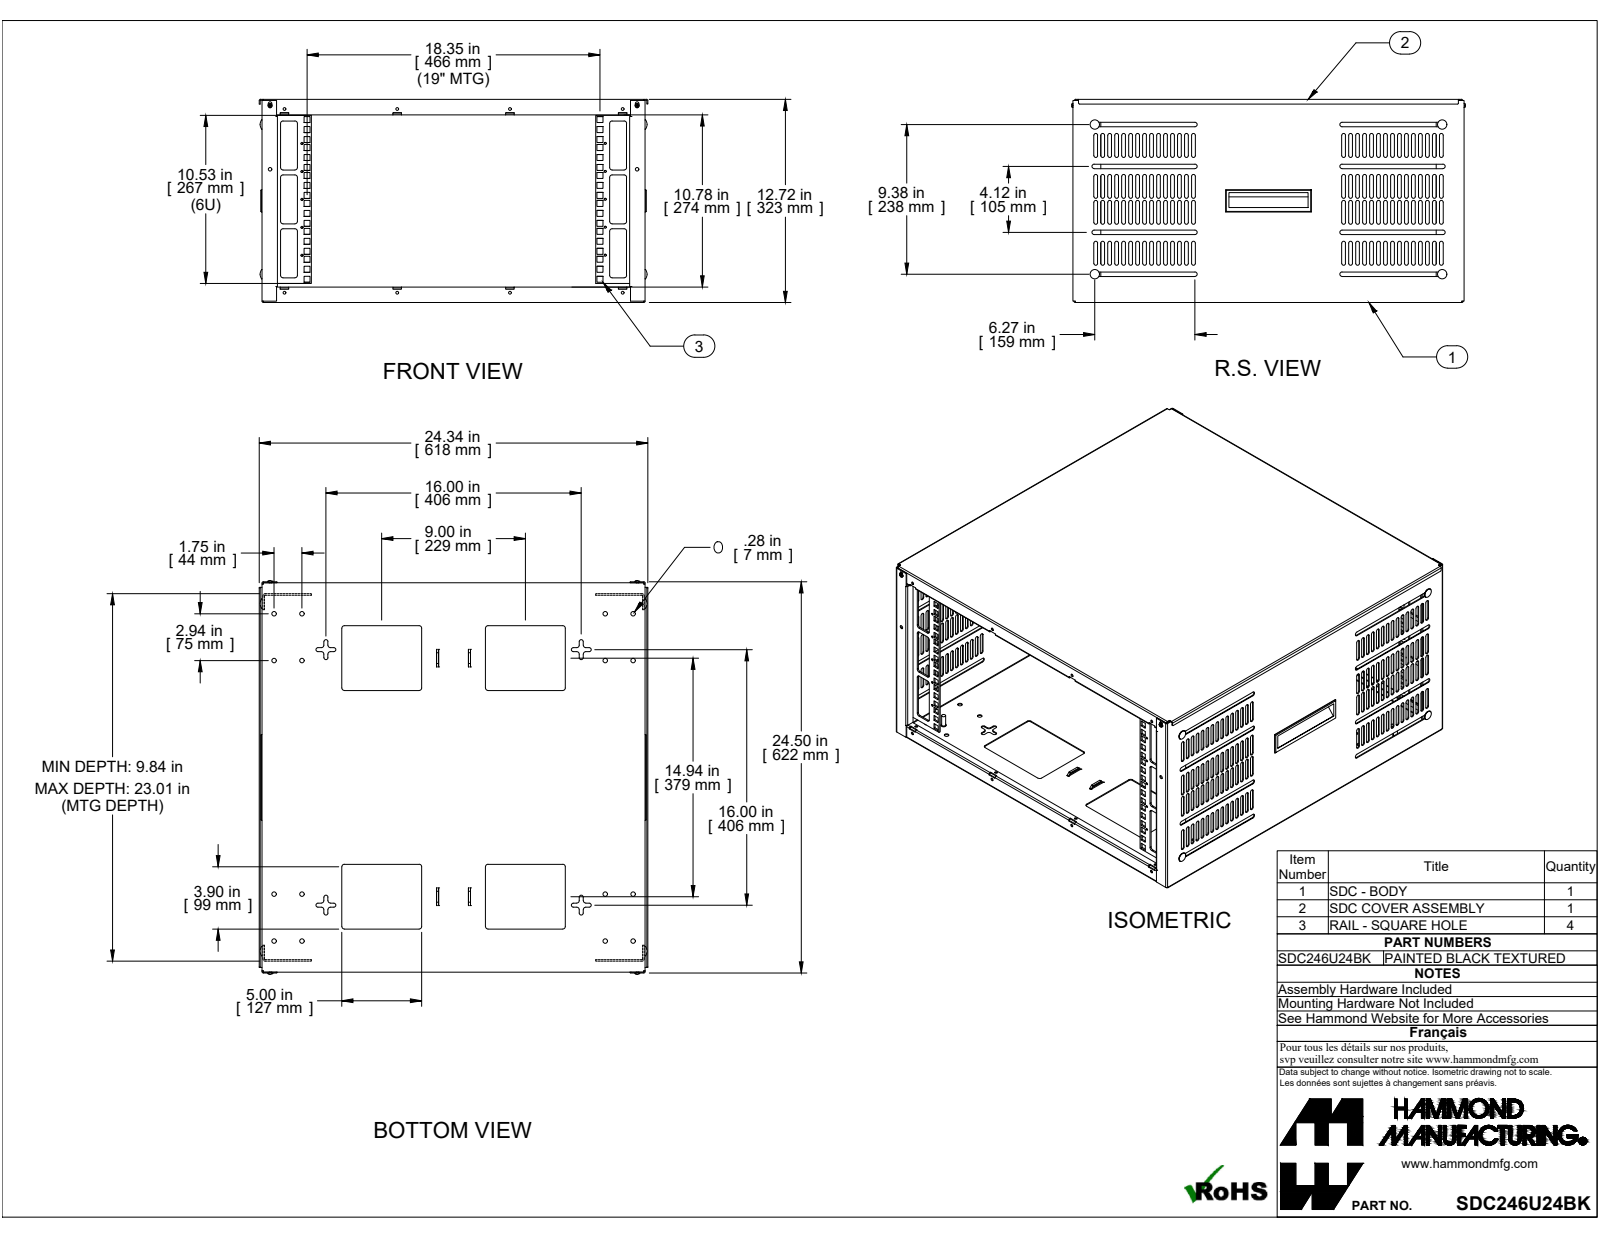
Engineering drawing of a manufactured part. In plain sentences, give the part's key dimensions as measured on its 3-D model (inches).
The part is named "SDC246U24BK". Its 3-D file was written by "SolidWorks 2019 (CONFIG_CONTROL_DESIGN)". It is 36 solids with 2622 faces: 1630 planar, 940 cylindrical and 52 other. Overall it measures 24.67 by 24.344 by 12.722 inches. Its volume is 121.3 cubic inches and its surface area 4 142 square inches. Round holes: 20 of diameter 0.125, 16 of diameter 0.17, 16 of diameter 0.281, 4 of diameter 0.196, 2 of diameter 0.159, 2 of diameter 0.187, 2 of diameter 0.213. Round bosses or shafts: 8 of diameter 0.25, 4 of diameter 0.58, 2 of diameter 0.313, 2 of diameter 0.28, 2 of diameter 0.187, 2 of diameter 0.138. Partial cylindrical surfaces (rounded edges, fillets, slot ends): 240 of radius 0.118, 60 of radius 0.157, 22 of radius 0.029, 22 of radius 0.086, 16 of radius 0.025, 16 of radius 0.125, 16 of radius 0.141, 12 of radius 0.117. The main face-to-face distances are 0.057, 12.665, 12.608, 12.722, 23.943, 23.886, 24, 0.072, 0.912, 0.095. The hole center spacings are 19.085, 1.75, 19.005, 19.324, 3.5, 2.937, 3.419, 7.063.
